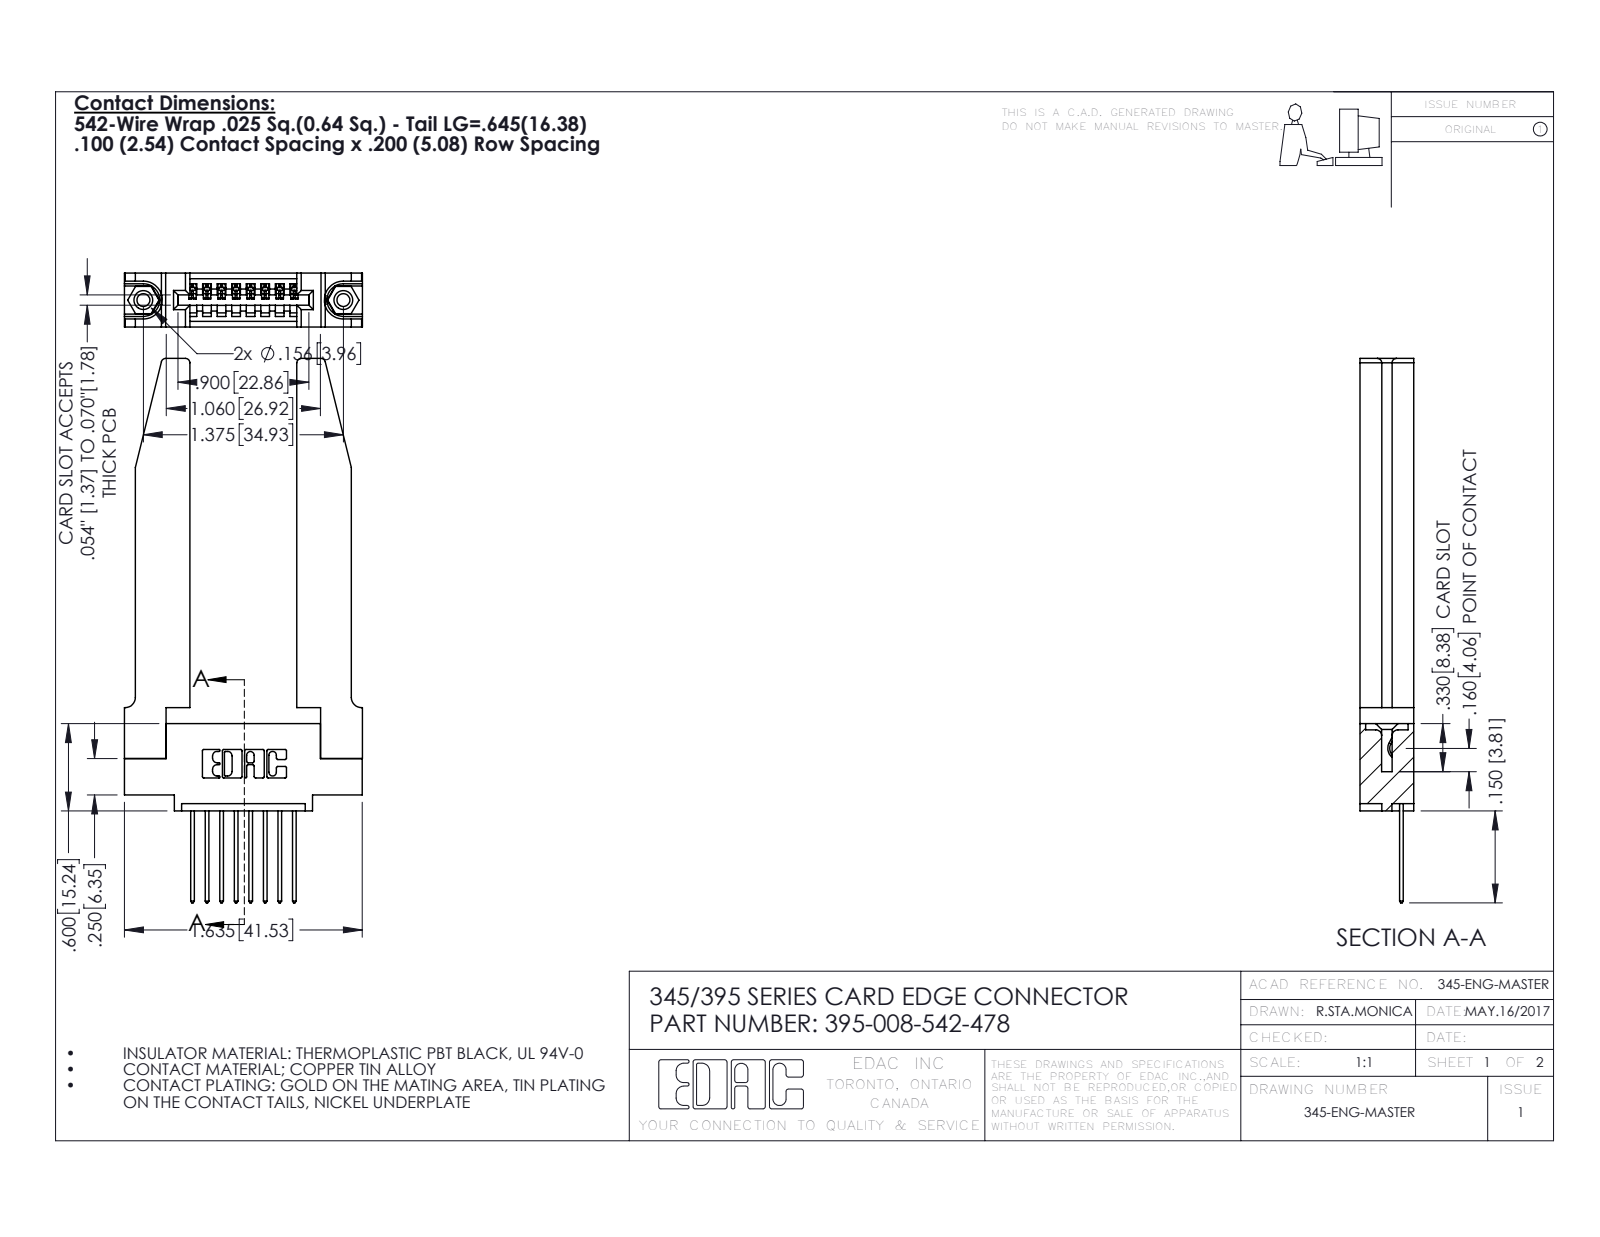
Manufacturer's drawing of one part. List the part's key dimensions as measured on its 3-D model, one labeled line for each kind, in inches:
Part name (STEP PRODUCT): 395-008-542-478; 345 Part_0.110 Offset - 0.156 Dia-TH; 345-250-001_345-250-001-102; 345-220-078_345-220-078 (+1 more)
STEP written by: SolidWorks 2016 (CONFIG_CONTROL_DESIGN)
Units: inches
Bodies: 13 solids, 828 faces (546 planar, 230 cylindrical, 52 other)
Overall size (bounding box): 3.742 × 1.636 × 0.37
Volume: 0.695 in³ · Surface area: 17.64 in²
Round holes (diameter × count): ⌀0.089 ×2, ⌀0.125 ×2, ⌀0.156 ×2, ⌀0.064 ×1
Round bosses / shafts (diameter × count): ⌀0.155 ×2
Partial cylindrical surfaces — rounded edges, fillets, slot ends (radius × count): R0.01 ×22, R0.006 ×16, R0.01 ×16, R0.03 ×8, R0.007 ×6, R0.031 ×6, R0.026 ×3, R0.031 ×2
Main face-to-face distances: 0.37, 0.072, 0.15, 0.298, 0.22, 0.148, 0.735, 0.077, 0.098, 0.272
Hole centre spacings: 0.27, 1.144, 1.375
